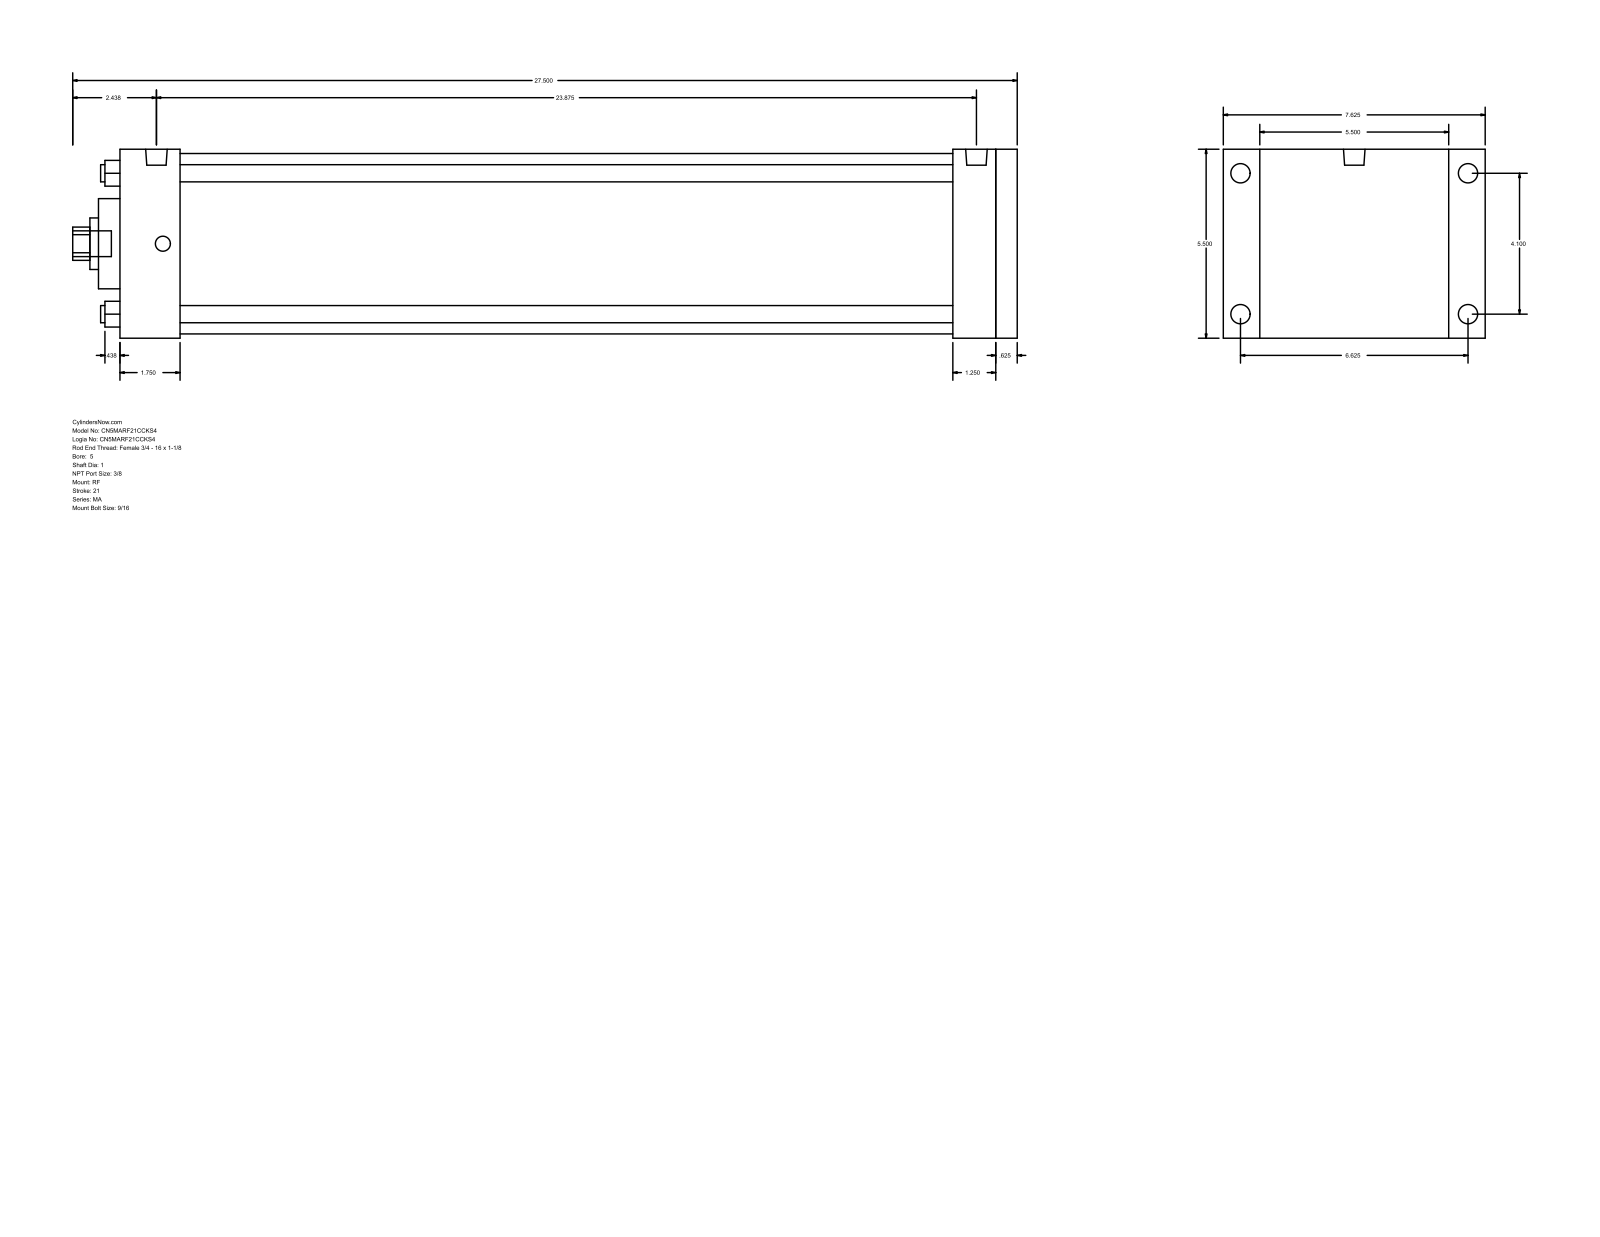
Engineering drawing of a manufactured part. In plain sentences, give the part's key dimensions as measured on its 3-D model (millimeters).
The part is named "MA_RF__0500_1". Its 3-D file was written by "GSSL Pune (CONFIG_CONTROL_DESIGN)". It is 0 solids with 94 faces: 65 planar, 29 cylindrical and 0 other. Overall it measures 698.5 by 193.68 by 139.7 millimeters. Round holes: 4 of diameter 12.7, 1 of diameter 25.4, 1 of diameter 38.1, 1 of diameter 66.67, 1 of diameter 133.35. Round bosses or shafts: 4 of diameter 14.29, 4 of diameter 11.11, 2 of diameter 15.93, 1 of diameter 19.05. Partial cylindrical surfaces (rounded edges, fillets, slot ends): 1 of radius 12.29. The main face-to-face distances are 139.7, 663.58, 647.7, 15.88, 44.46, 603.24, 619.12, 615.96, 571.5, 31.74. The hole center spacings are 73.64, 104.14, 147.28.
